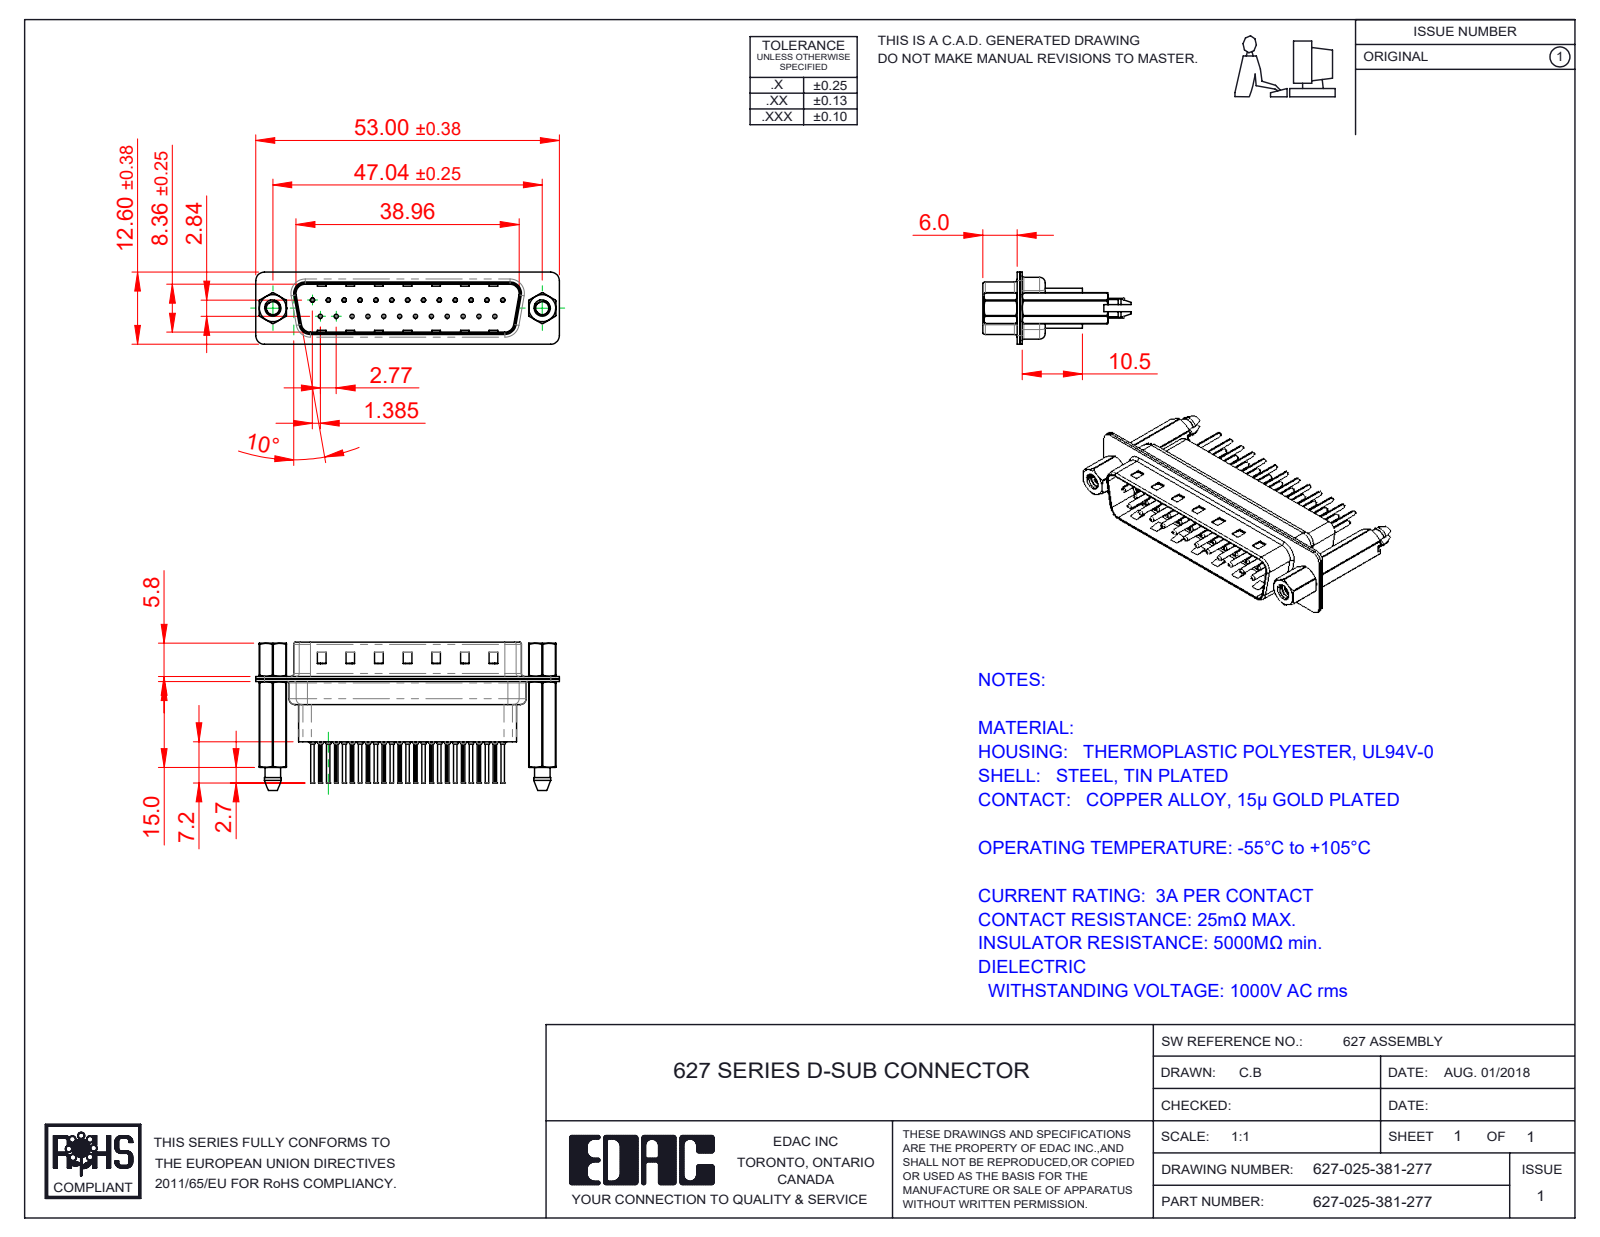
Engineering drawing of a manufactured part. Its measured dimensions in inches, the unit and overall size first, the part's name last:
Units: inches
Overall size (bounding box): 2.087 × 1.02 × 0.496
Round holes (diameter × count): ⌀0.008 ×25, ⌀0.014 ×25, ⌀0.043 ×25, ⌀0.063 ×25, ⌀0.089 ×2, ⌀0.09 ×2, ⌀0.157 ×2, ⌀0.189 ×2
Round bosses / shafts (diameter × count): ⌀0.079 ×25, ⌀0.059 ×25, ⌀0.03 ×25, ⌀0.024 ×25, ⌀0.193 ×2, ⌀0.11 ×2
Partial cylindrical surfaces — rounded edges, fillets, slot ends (radius × count): R0.004 ×50, R0.059 ×18, R0.079 ×12, R0.063 ×10, R0.02 ×8, R0.01 ×4, R0.024 ×4, R0.026 ×4
Main face-to-face distances: 0.016, 0.018, 0.032, 0.377, 0.027, 0.302, 0.059, 0.035, 0.043, 0.318
Hole centre spacings: 0.124, 0.327, 0.109, 0.218, 0.436, 0.654, 0.198, 0.198
Volume: 0.27 in³ · Surface area: 17.54 in²
Bodies: 32 solids, 3060 faces (825 planar, 1200 cylindrical, 1035 other)
Part name (STEP PRODUCT): 627 Shell Front_25 Contacts; 627 4-40 Threaded Boardlock_HP81; 627-025-381-277; 627 4-40 Hex Standoff (+4 more)
STEP written by: SolidWorks 2020 (CONFIG_CONTROL_DESIGN)
